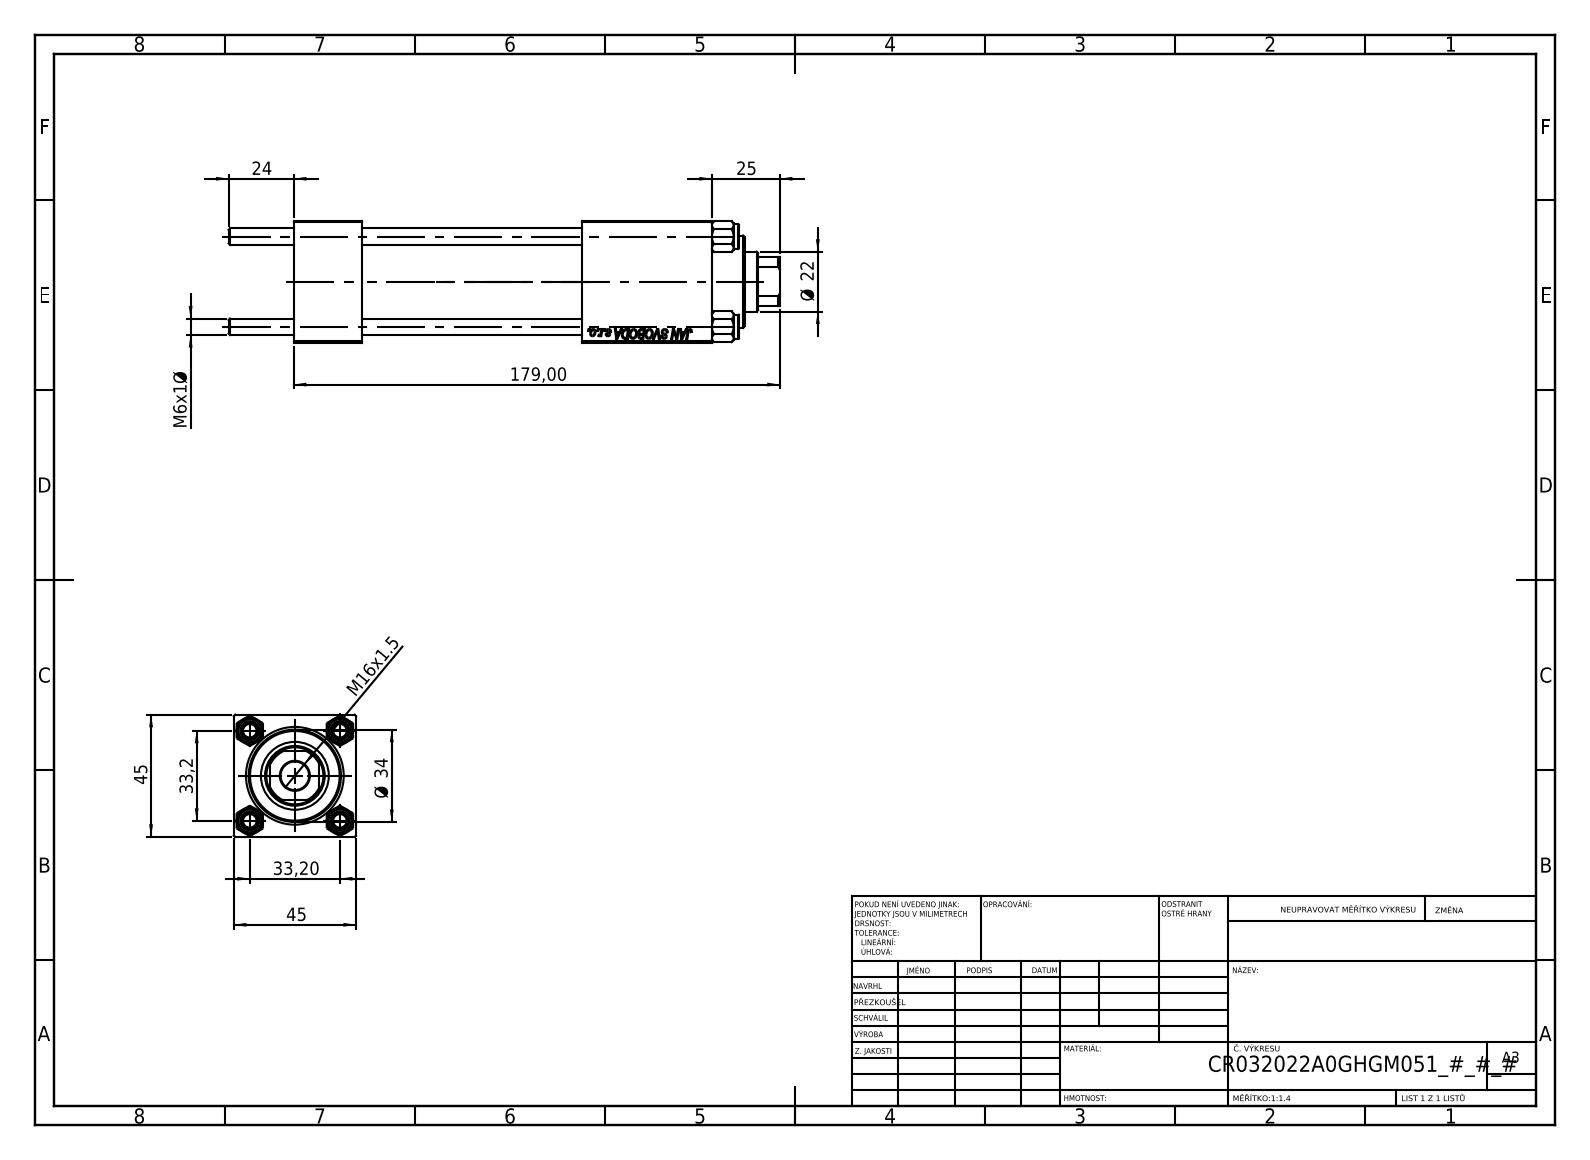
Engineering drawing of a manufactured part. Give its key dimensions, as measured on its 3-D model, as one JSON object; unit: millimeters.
{"part_name": "NUT_M5; V215CR_VCP; CR025_012_A_0_G_A_G_M_020_+#_##_TYCINKA; V215_VC_A (+1 more)", "step_written_by": "SolidWorks 2019 (CONFIG_CONTROL_DESIGN)", "units": "millimeters", "bodies": {"solids": 11, "faces": 1133, "planar": 519, "cylindrical": 78, "other": 536}, "overall_size": [203, 45, 45], "volume_mm3": 239790, "surface_area_mm2": 88339, "round_holes": [[6, 4], [7, 2], [13.16, 2], [20, 2], [10.5, 1], [22, 1], [24, 1], [25, 1], [32, 1], [33, 1]], "round_bosses_or_shafts": [[9, 4], [38, 1], [34, 1]], "partial_cylinders_radius": [[10.5, 1]], "face_to_face_distances": [45, 25, 154, 106, 81, 129, 48, 125.3, 100.3, 19.3], "hole_center_spacings": [23.48, 33.2, 46.95, 106.5]}
